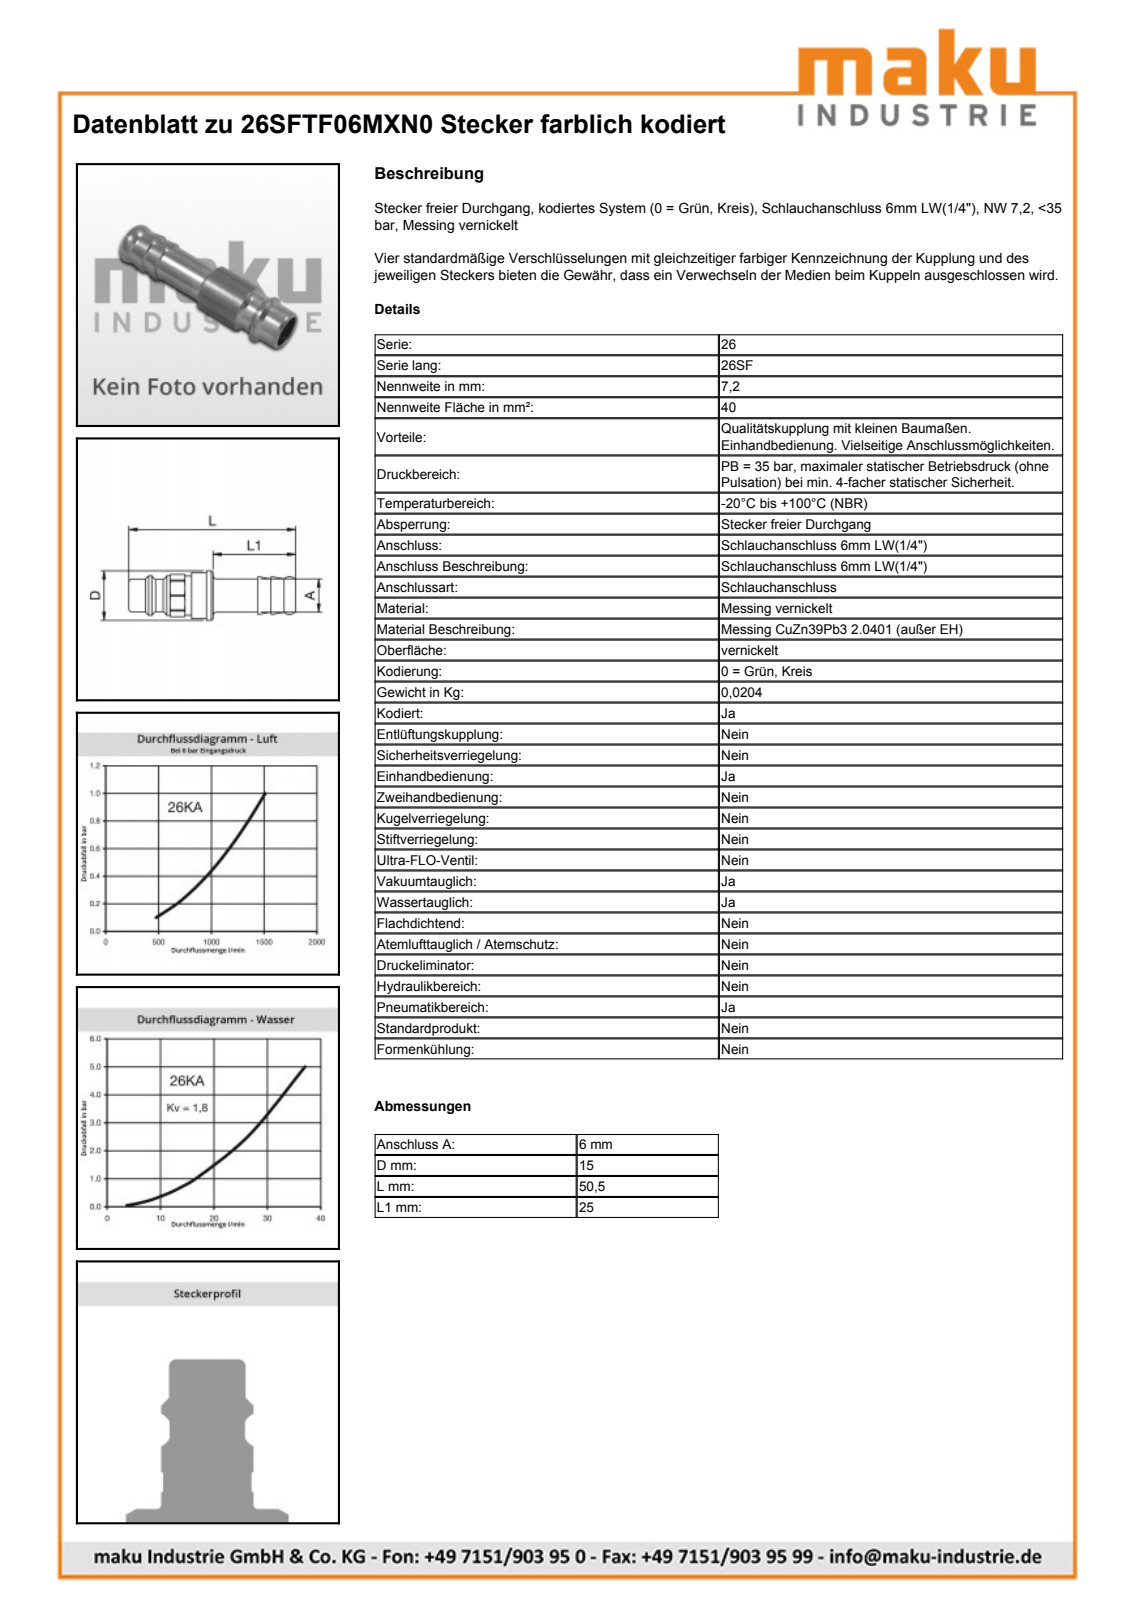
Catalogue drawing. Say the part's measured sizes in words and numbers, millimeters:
The part is named "D103818; D103784; D103012". Its 3-D file was written by "Autodesk Inventor 2011 (AUTOMOTIVE_DESIGN)". It is 2 solids with 39 faces: 9 planar, 13 cylindrical and 17 other. Overall it measures 50.5 by 15.5 by 15.5 millimeters. Its volume is 2 412 cubic millimeters and its surface area 3 147 square millimeters. Round holes: 1 of diameter 4.1, 1 of diameter 7.85, 1 of diameter 13.85, 1 of diameter 14.05. Round bosses or shafts: 1 of diameter 15.5, 1 of diameter 15, 1 of diameter 14, 1 of diameter 12.5, 1 of diameter 12, 1 of diameter 10, 1 of diameter 9.75, 1 of diameter 6.1. The main face-to-face distances are 2, 6.2, 4.2, 6.5, 4.5, 25, 27, 31.2, 31.5, 11.5.
